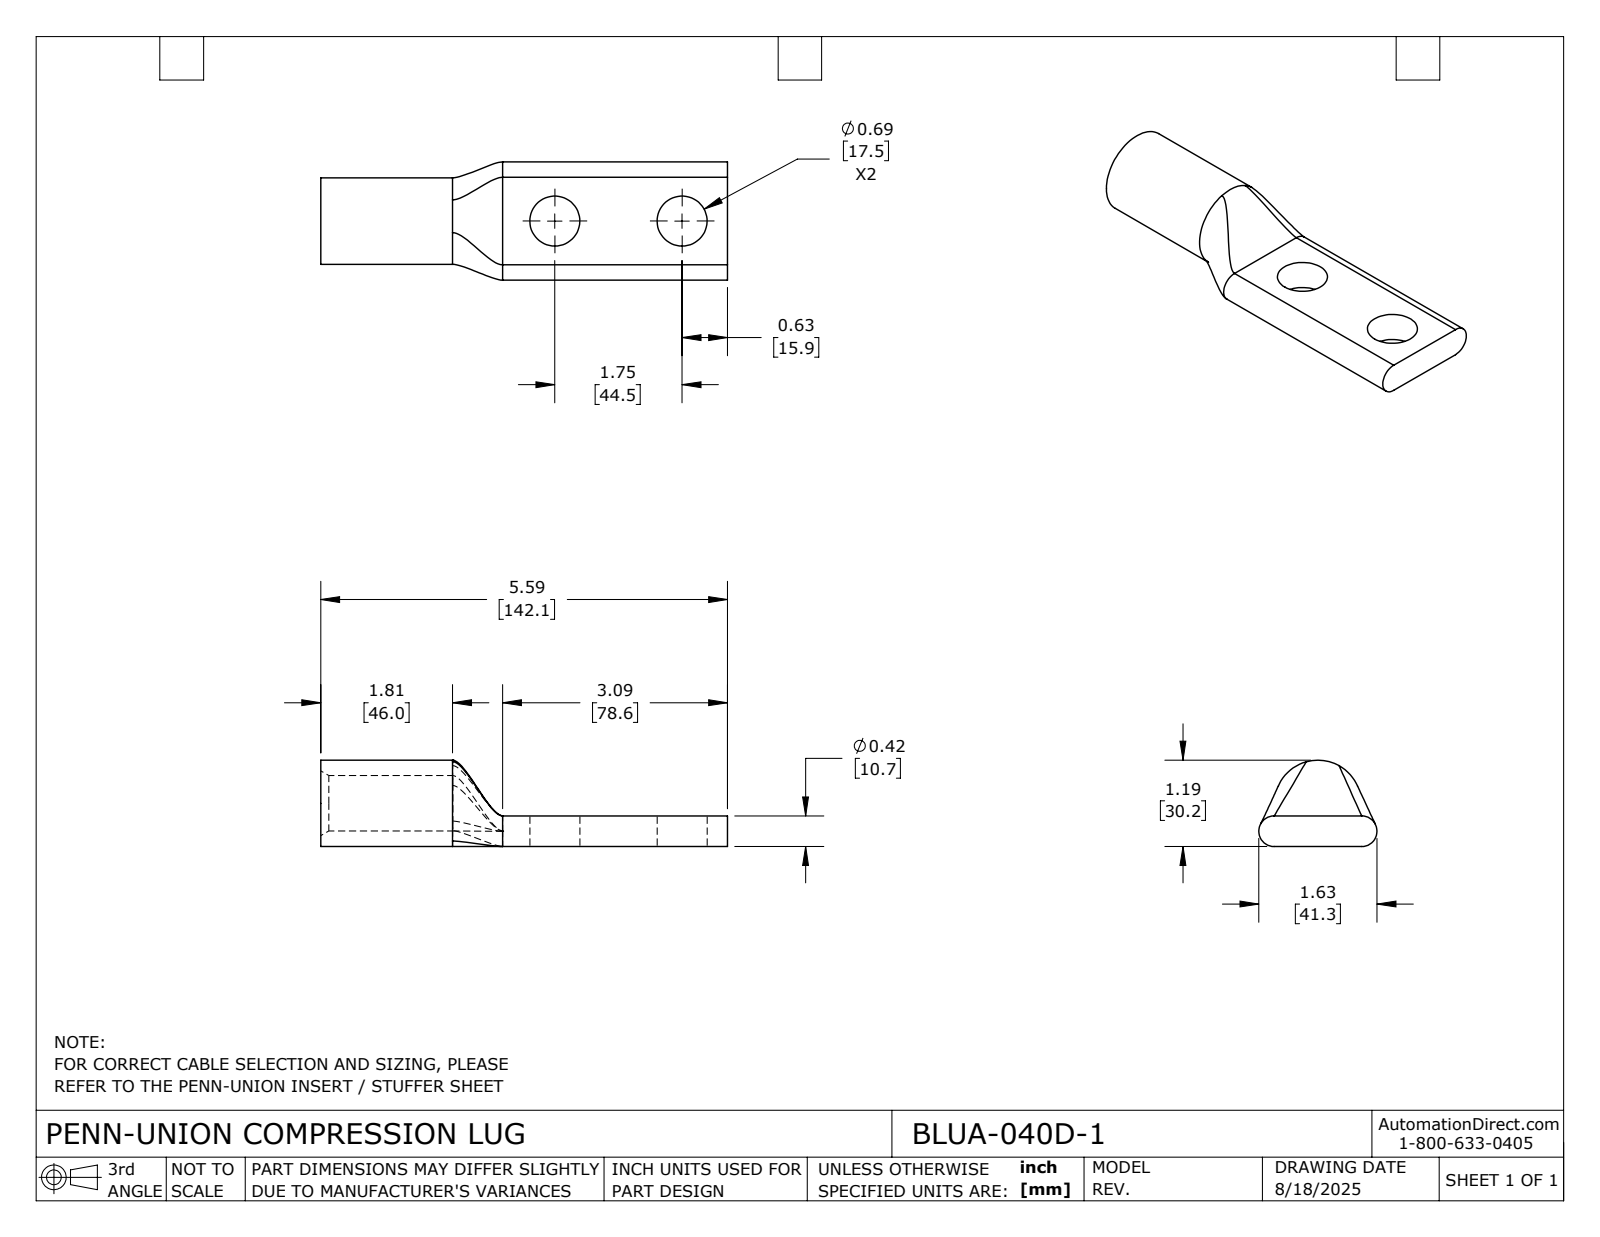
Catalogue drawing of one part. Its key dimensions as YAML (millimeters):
part_name: "BLUA-040D-1"
step_written_by: "SolidWorks 2024 (CONFIG_CONTROL_DESIGN)"
units: millimeters
bodies: {solids: 1, faces: 26, planar: 5, cylindrical: 11, other: 10}
overall_size: [142.1, 41.3, 30.2]
volume: 54190
surface_area: 18750
round_holes:
  - {diameter: 17.4, count: 2}
  - {diameter: 19.4, count: 1}
round_bosses_or_shafts:
  - {diameter: 30.2, count: 1}
partial_cylinders:
  - {radius: 5.4, count: 2}
face_to_face_distances: [10.7, 142.1, 63.5, 78.6]
hole_center_spacings: [44.5]
